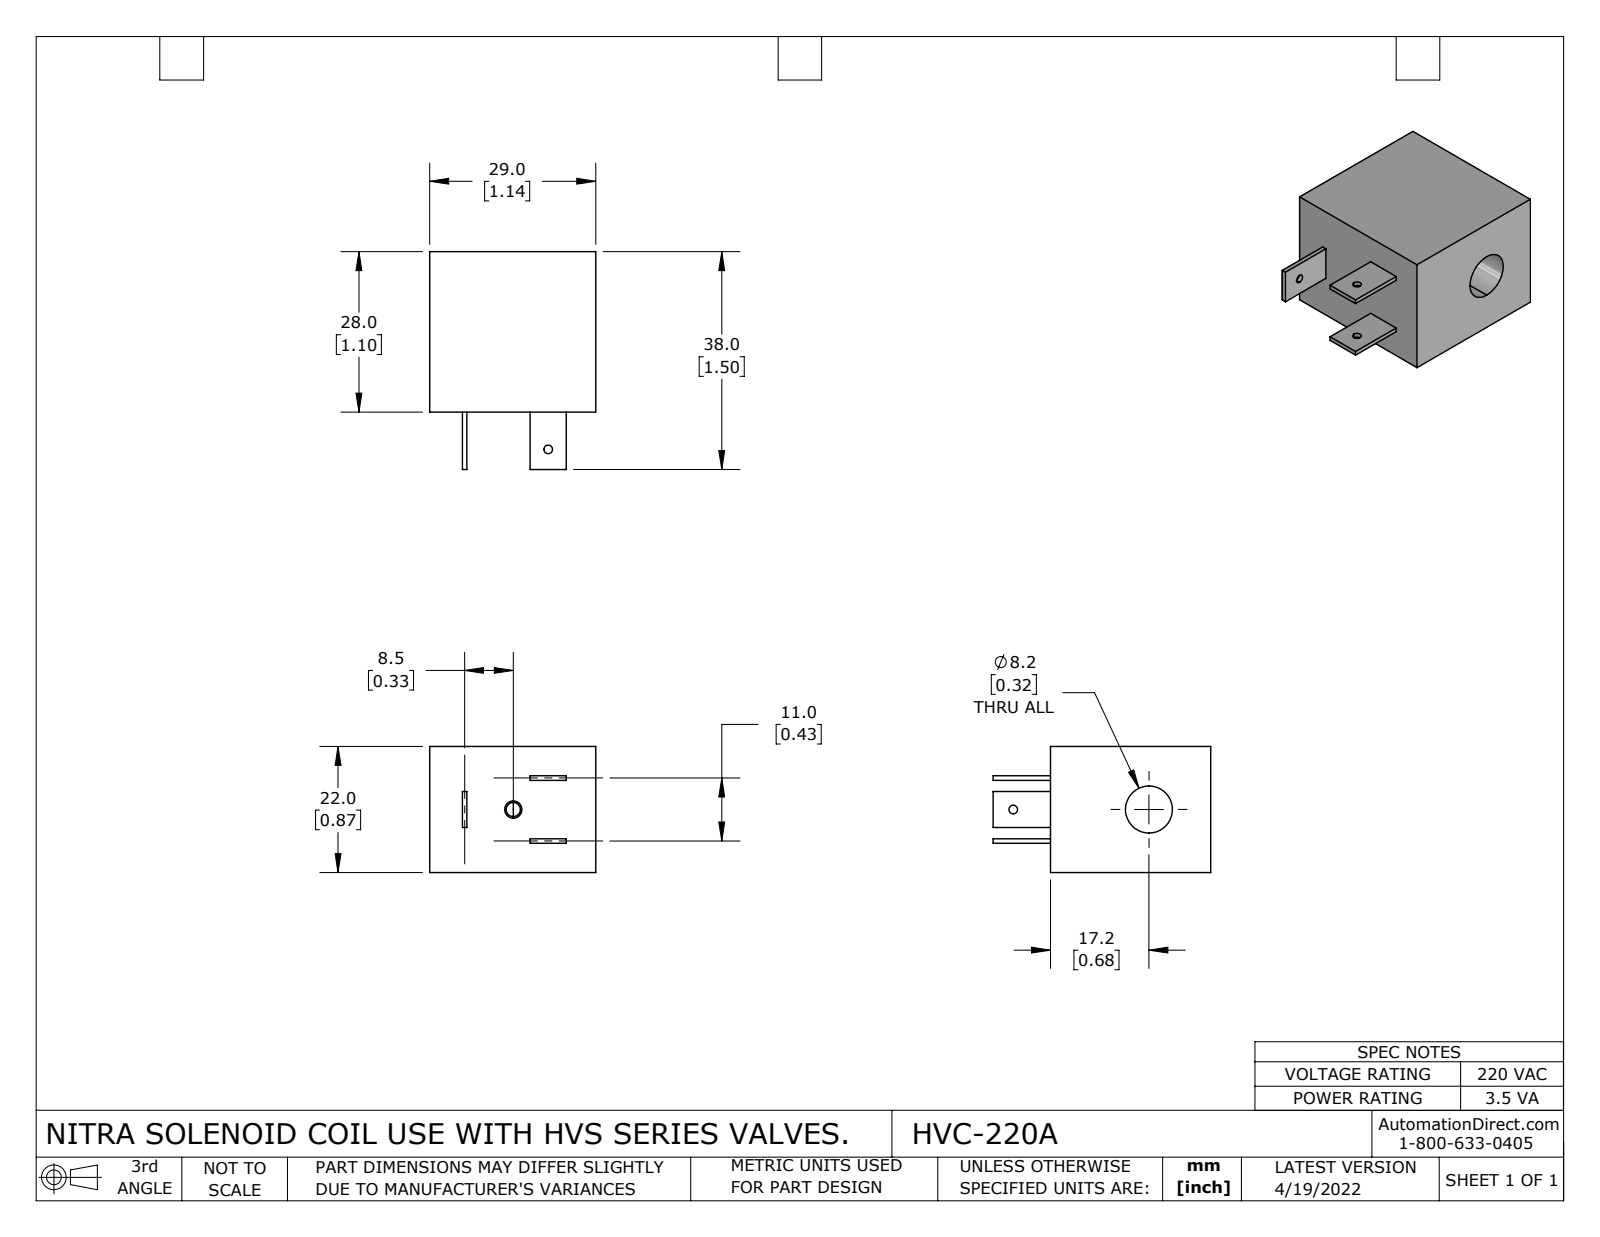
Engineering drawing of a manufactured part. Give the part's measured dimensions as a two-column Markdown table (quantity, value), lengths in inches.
| quantity | value |
| --- | --- |
| part name | HVC-220A |
| STEP written by | SolidWorks 2021 (CONFIG_CONTROL_DESIGN) |
| units | inches |
| bodies | 1 solid, 35 faces (21 planar, 10 cylindrical, 4 other) |
| overall size | 1.496 × 1.142 × 0.866 |
| volume | 1.004 in³ |
| surface area | 8.119 in² |
| round holes (diameter × count) | 0.059 × 2, 0.097 × 1, 0.323 × 1 |
| main face-to-face distances | 0.866, 1.102, 1.142, 0.031, 0.201, 0.232, 0.634, 0.665, 0.433, 0.224 |
| hole center spacings | 0.933 |
